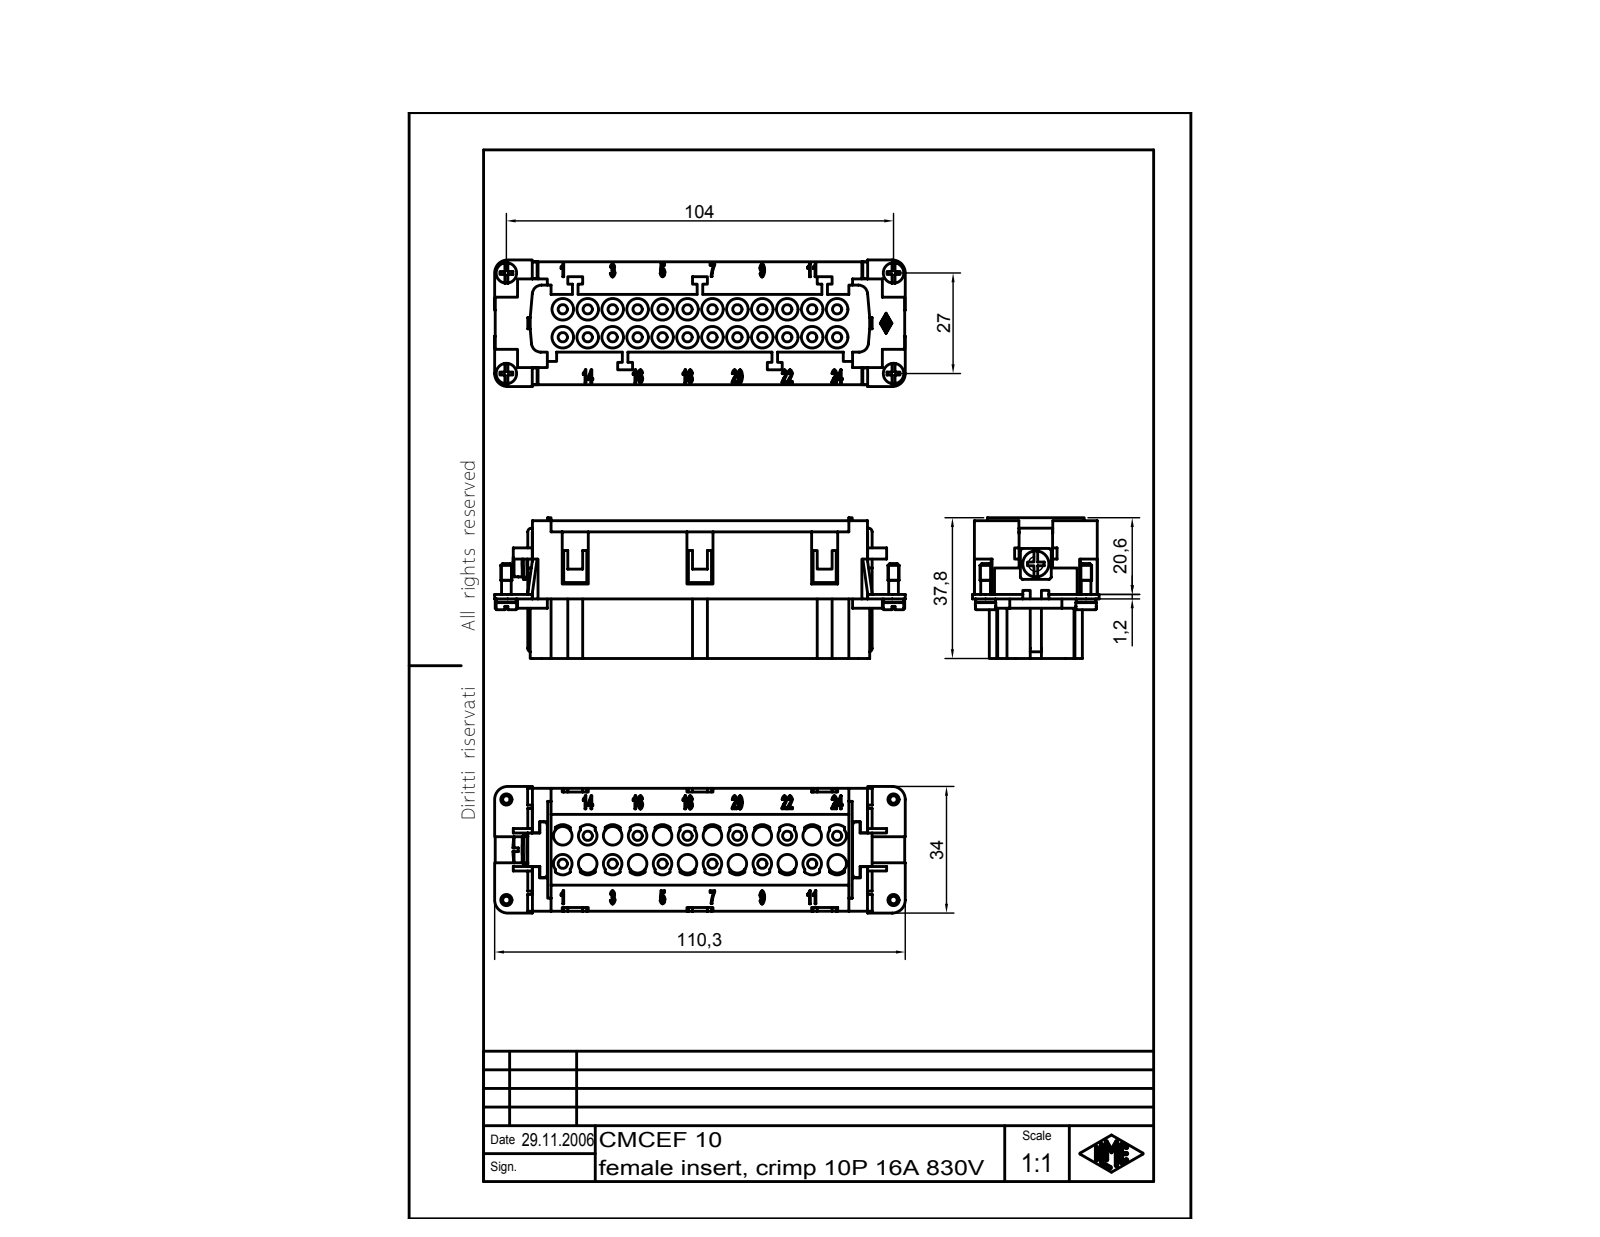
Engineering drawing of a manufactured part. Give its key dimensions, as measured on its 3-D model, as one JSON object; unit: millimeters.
{"part_name": "CMCEF 10", "step_written_by": "Autodesk Inventor 7 (AUTOMOTIVE_DESIGN)", "units": "millimeters", "bodies": {"solids": 1, "faces": 1375, "planar": 591, "cylindrical": 114, "other": 670}, "overall_size": [110.3, 37.8, 34], "volume_mm3": 75119, "surface_area_mm2": 31421, "round_holes": [[5, 6], [3.24, 1], [7, 1]], "round_bosses_or_shafts": [[5.5, 2], [5.3, 2], [3, 2], [2.6, 2]], "partial_cylinders_radius": [[2.5, 16], [0.1, 14], [3, 12], [1, 4], [3.5, 2], [5.5, 1]], "face_to_face_distances": [24.25, 8.75, 3, 21, 33, 15.5, 18, 1, 16, 37], "hole_center_spacings": [13.4, 26.8, 40.2, 53.6, 67]}
